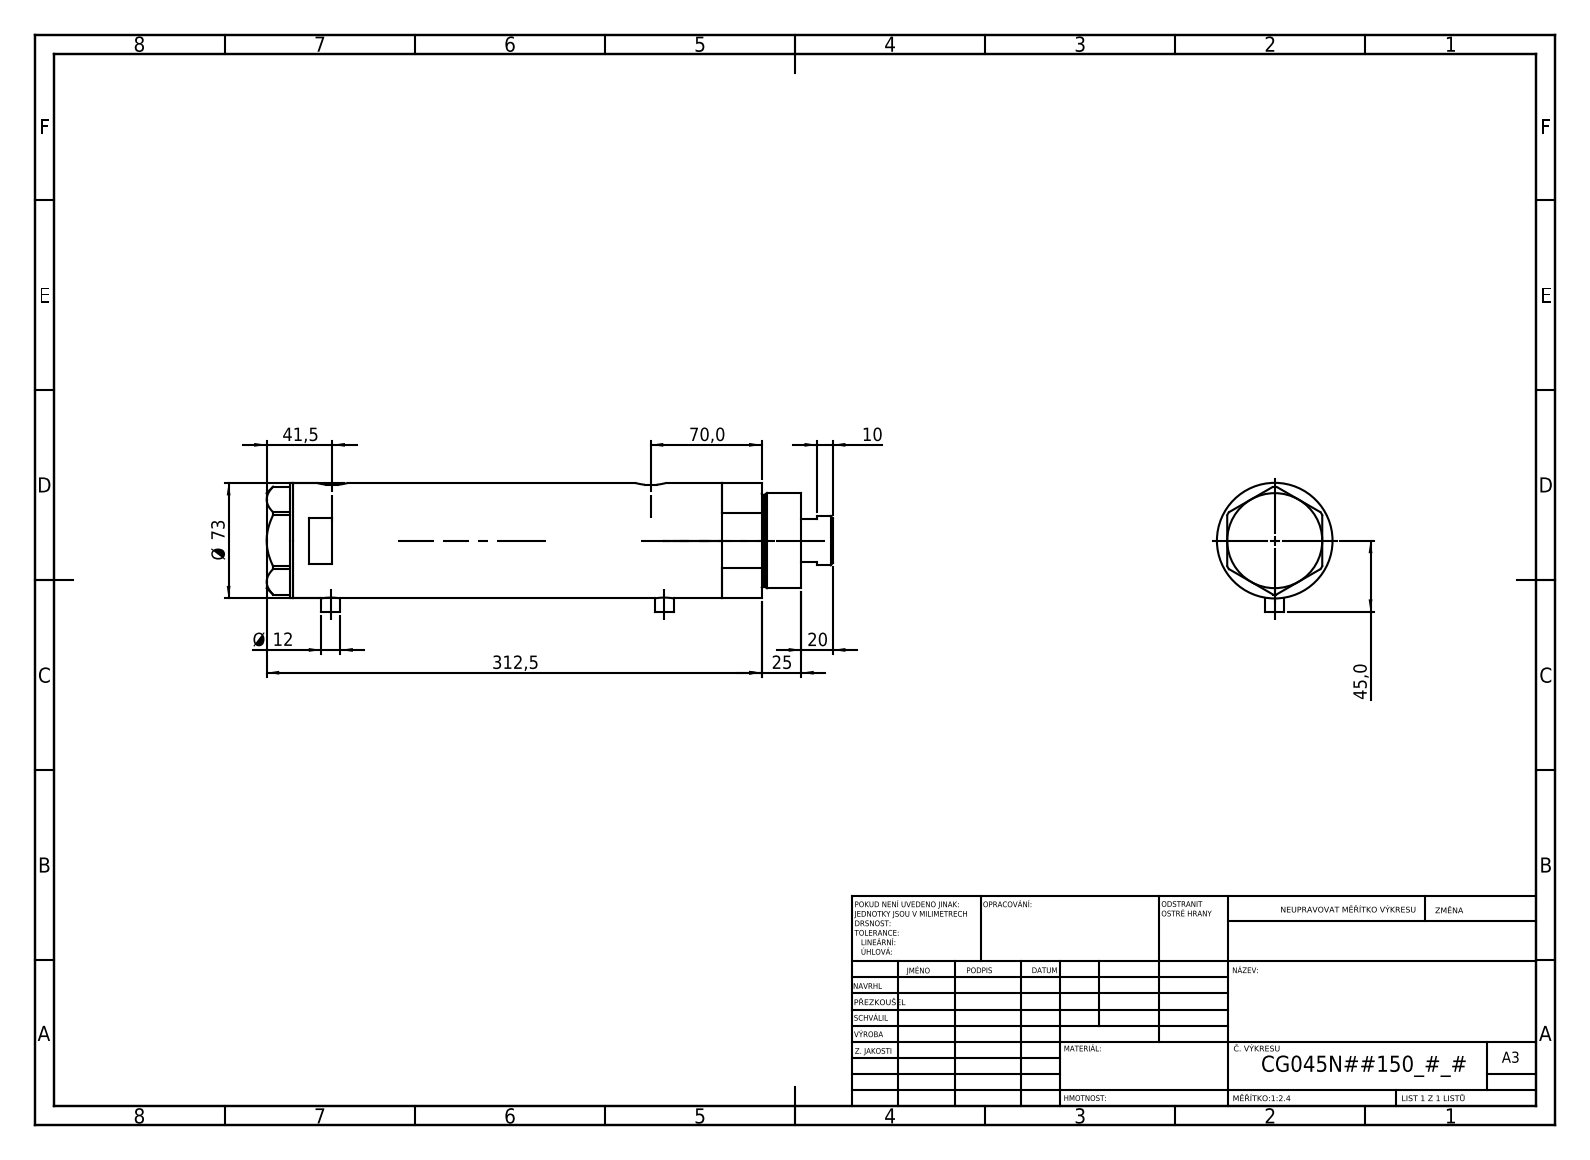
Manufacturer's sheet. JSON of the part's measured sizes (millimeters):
{"part_name": "V270CG_BACK; V270CG_MIDDLE; V270CG_FRONT; V270CG_VC", "step_written_by": "SolidWorks 2019 (CONFIG_CONTROL_DESIGN)", "units": "millimeters", "bodies": {"solids": 4, "faces": 120, "planar": 49, "cylindrical": 51, "other": 20}, "overall_size": [357.5, 81.5, 73], "volume_mm3": 1247000, "surface_area_mm2": 198635, "round_holes": [[12.5, 2], [13.16, 2], [10.5, 1], [32, 1], [33.5, 1], [45, 1], [48, 1], [64, 1]], "round_bosses_or_shafts": [[12, 2], [73, 1], [60, 1], [58, 1], [31, 1]], "partial_cylinders_radius": [[10, 2]], "face_to_face_distances": [226, 26, 200, 16.5, 42.5, 242.5, 2, 321, 337.5, 295], "hole_center_spacings": [1, 8.5, 201, 202, 209.5, 210.5]}
